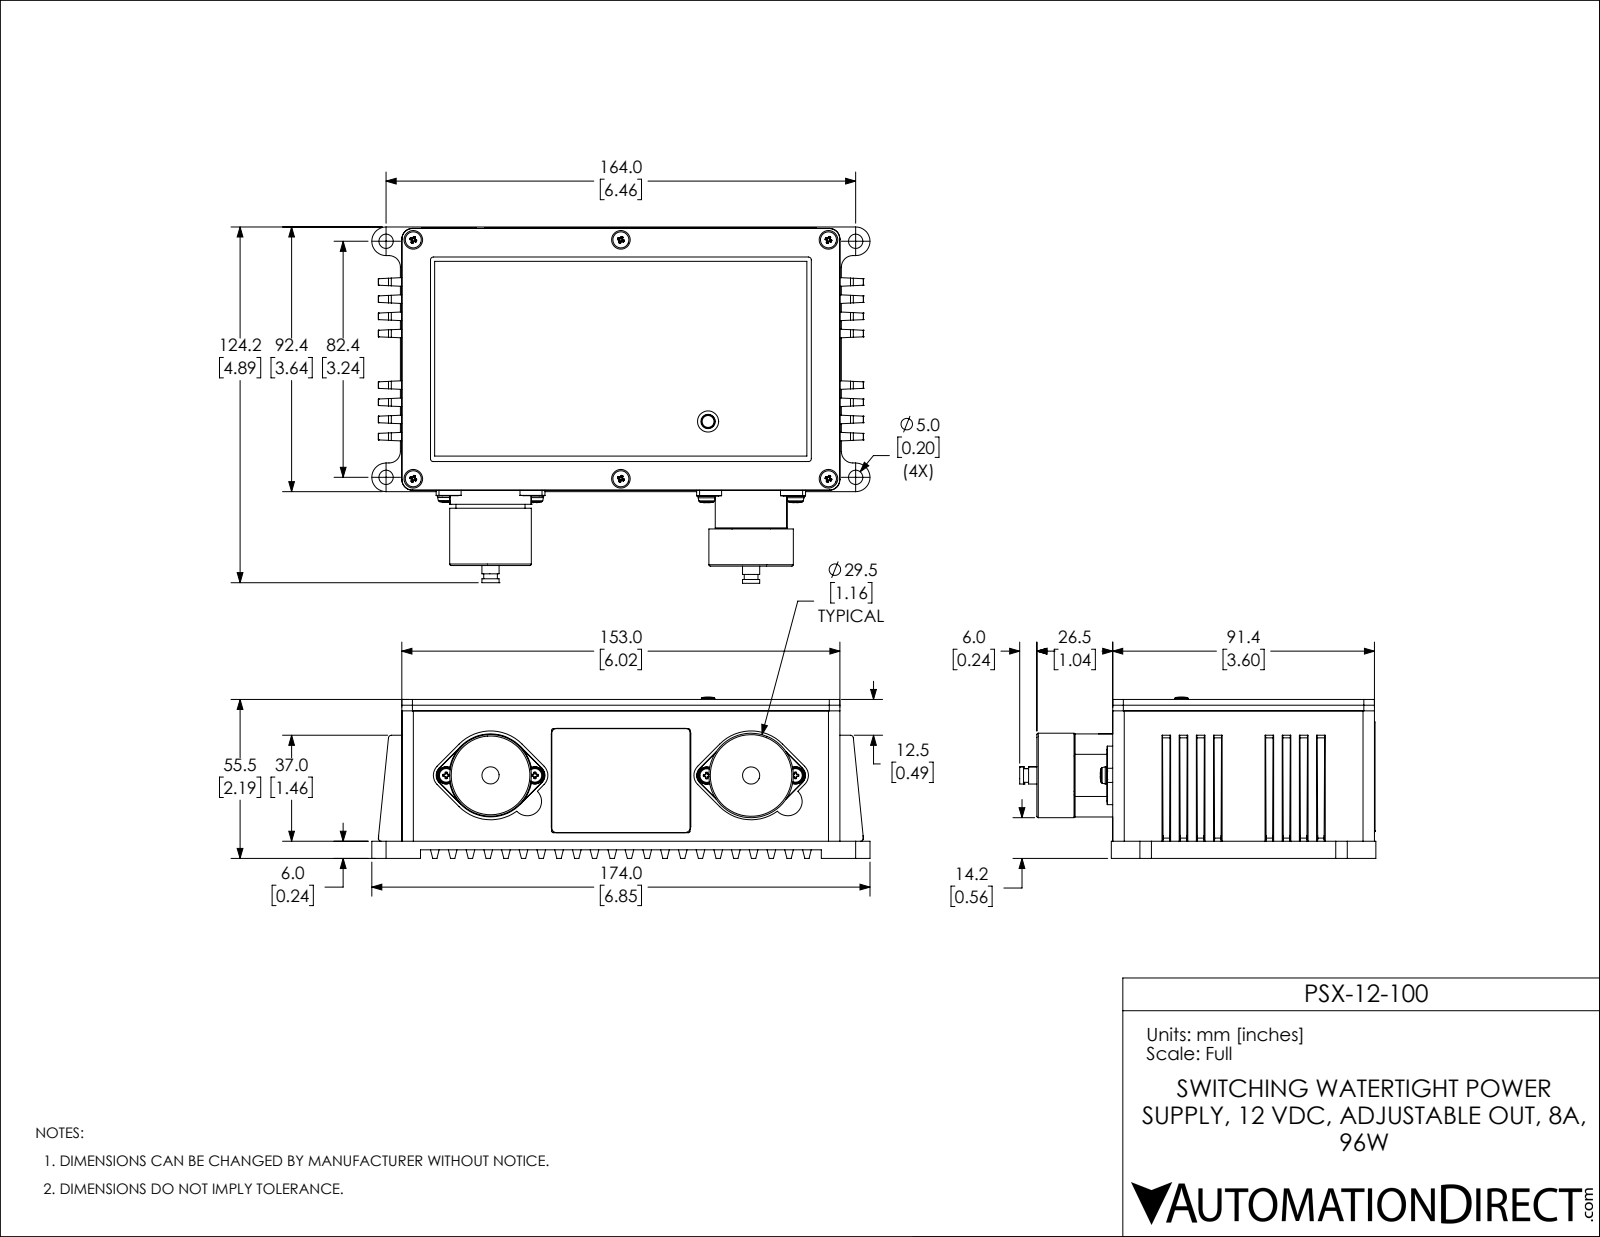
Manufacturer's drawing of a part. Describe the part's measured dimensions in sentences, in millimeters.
The part is named "PSX". Its 3-D file was written by "SolidWorks 2017 (AUTOMOTIVE_DESIGN)". It is 21 solids with 1198 faces: 768 planar, 270 cylindrical and 160 other. Overall it measures 174 by 124.4 by 56.4 millimeters. Its volume is 262 800 cubic millimeters and its surface area 172 900 square millimeters. Round holes: 11 of diameter 1.5, 6 of diameter 3.2, 5 of diameter 5, 4 of diameter 3, 4 of diameter 3.5, 4 of diameter 4, 2 of diameter 0.8, 2 of diameter 2, 2 of diameter 22, 1 of diameter 7.4, 1 of diameter 13.7, 1 of diameter 17. Round bosses or shafts: 10 of diameter 3, 7 of diameter 2, 6 of diameter 5.6, 4 of diameter 2.5, 2 of diameter 6, 2 of diameter 4.8, 1 of diameter 29.5, 1 of diameter 29. Partial cylindrical surfaces (rounded edges, fillets, slot ends): 32 of radius 0.2, 26 of radius 0.1, 24 of radius 0.4, 8 of radius 1, 7 of radius 4, 6 of radius 0.3, 6 of radius 5, 4 of radius 2.2. The main face-to-face distances are 3.8, 5, 4, 3, 49.5, 49.3, 45.5, 86.4, 91.4, 52.5. The hole center spacings are 15.5, 4.5, 4.7, 4.8, 6.4, 9.5, 16.1, 31.
